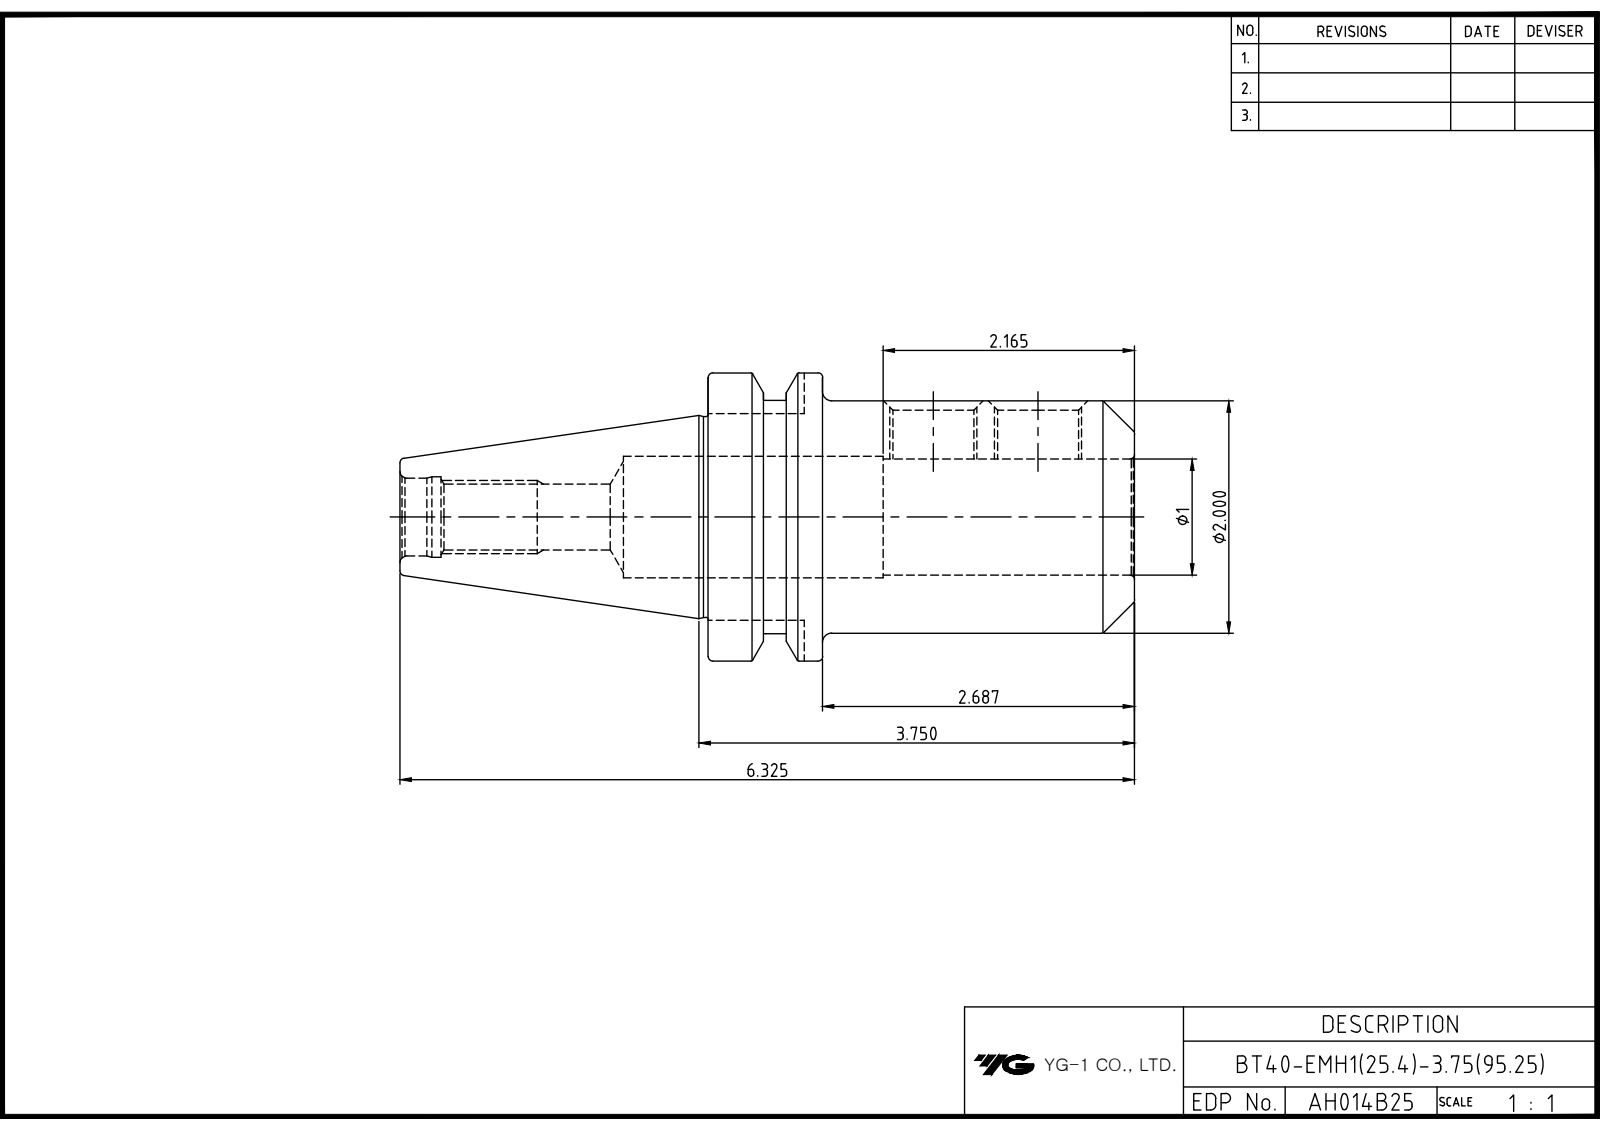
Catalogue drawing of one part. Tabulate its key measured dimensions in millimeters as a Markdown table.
| quantity | value |
| --- | --- |
| part name | LO-BT40-EMH25.4-95.25 |
| STEP written by | Autodesk Inventor 2022 (AUTOMOTIVE_DESIGN) |
| units | millimeters |
| bodies | 1 solid, 55 faces (18 planar, 16 cylindrical, 21 other) |
| overall size | 160.65 × 63 × 63 |
| volume | 194 687 mm³ |
| surface area | 40 060 mm² |
| round holes (diameter × count) | 17.32 × 2, 13.84 × 1, 17 × 1, 17.6 × 1, 25.4 × 1, 26.6 × 1 |
| round bosses / shafts (diameter × count) | 63 × 1, 52.6 × 1, 50.8 × 1, 44 × 1 |
| partial cylindrical surfaces (radius × count) | 8.05 × 1 |
| main face-to-face distances | 25, 93.25, 68.25, 45.2, 16.1, 67.4, 92.4, 160.65, 84.5, 17.1 |
| hole center spacings | 22.9 |
